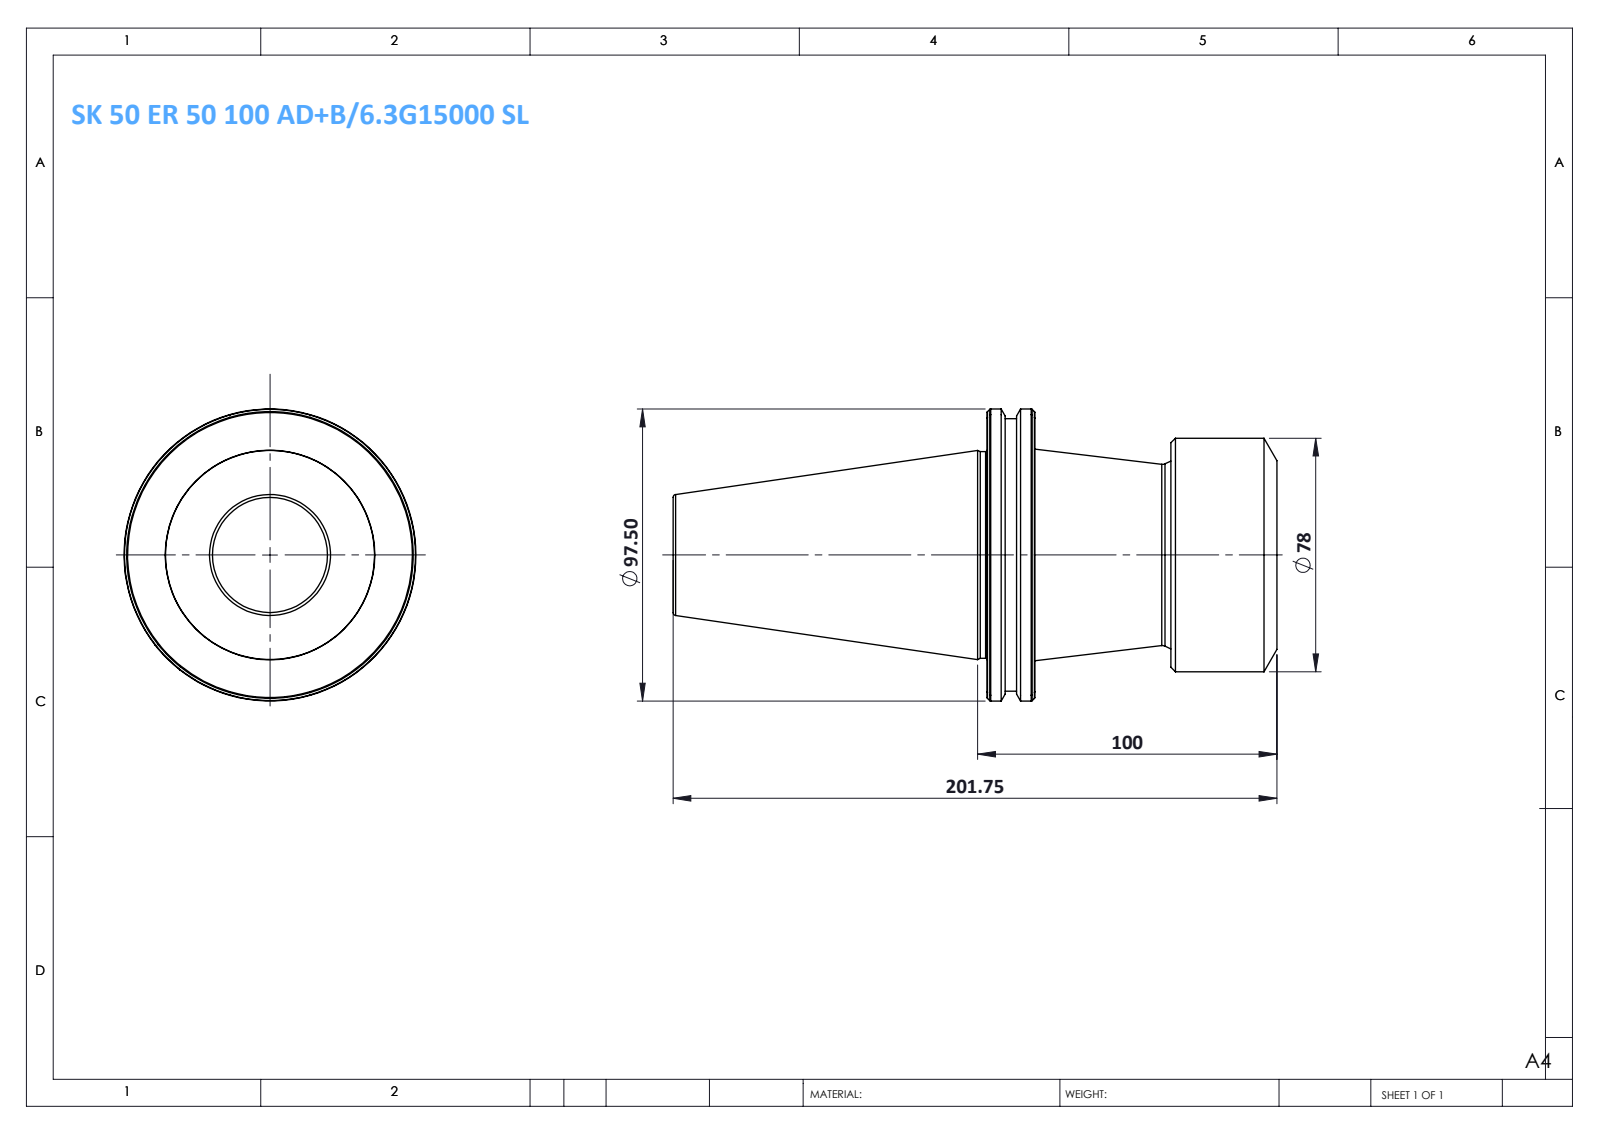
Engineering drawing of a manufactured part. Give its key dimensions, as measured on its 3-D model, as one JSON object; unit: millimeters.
{"part_name": "SK 50 ER 50 100 AD-6.3G15000 SL", "step_written_by": "SolidWorks 2014 (CONFIG_CONTROL_DESIGN)", "units": "millimeters", "bodies": {"solids": 1, "faces": 71, "planar": 7, "cylindrical": 10, "other": 54}, "overall_size": [201.75, 97.5, 97.5], "volume_mm3": 691429, "surface_area_mm2": 56230, "round_bosses_or_shafts": [[97.5, 1], [91, 1], [78, 1], [69, 1]], "face_to_face_distances": [15.9, 80.9, 96.8, 35.4, 45.5, 61.4, 201.75, 166.35, 120.85, 104.95]}
